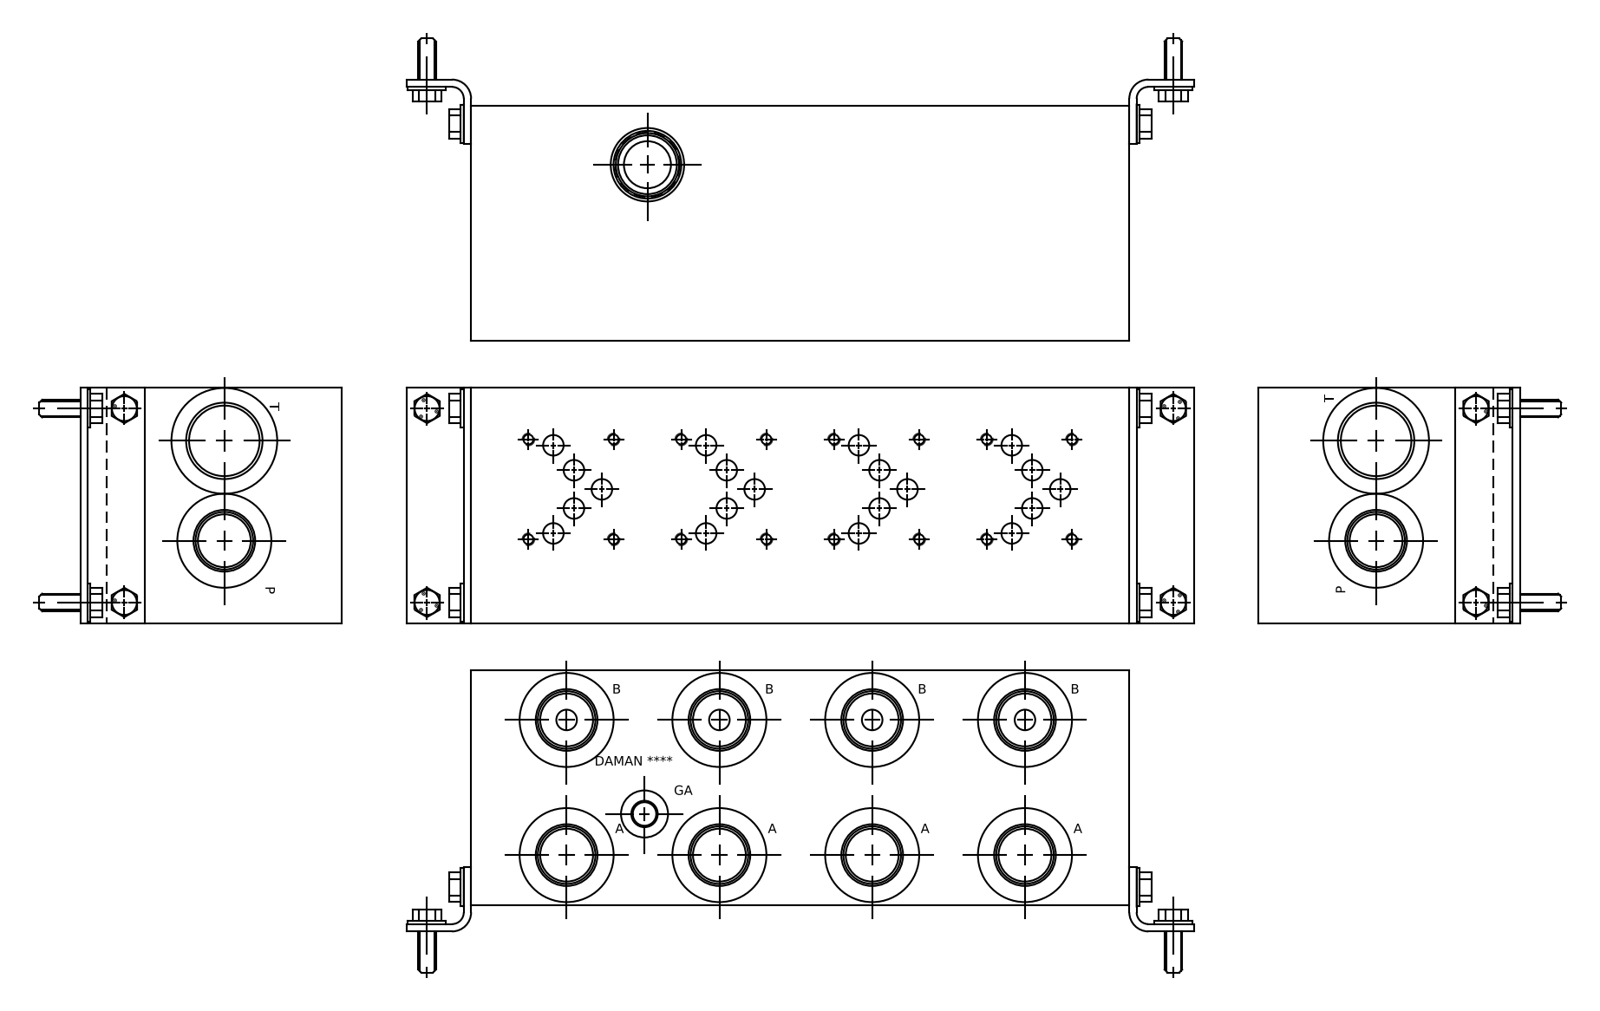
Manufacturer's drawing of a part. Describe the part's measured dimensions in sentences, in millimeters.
The part is named "Part_DD05JP043S~S_3D". Its 3-D file was written by "Autodesk Inventor 2019 (AUTOMOTIVE_DESIGN)". It is 1 solid with 865 faces: 429 planar, 138 cylindrical and 298 other. Overall it measures 355.6 by 127 by 127 millimeters. Its volume is 5 242 000 cubic millimeters and its surface area 280 857 square millimeters. Round holes: 16 of diameter 5.11, 16 of diameter 6.35, 9 of diameter 31.27, 9 of diameter 33.34, 9 of diameter 33.76, 9 of diameter 48.97, 8 of diameter 10.31, 8 of diameter 11.13, 8 of diameter 28.57, 7 of diameter 35.51, 6 of diameter 9.53, 2 of diameter 7.92. The main face-to-face distances are 127, 0.79, 355.6, 126.21, 354.81, 354.02, 19.05, 19.84, 107.16, 335.76. The hole center spacings are 82.55, 165.1, 247.65, 60.3, 72.71, 85.09, 18.28, 35.4.
